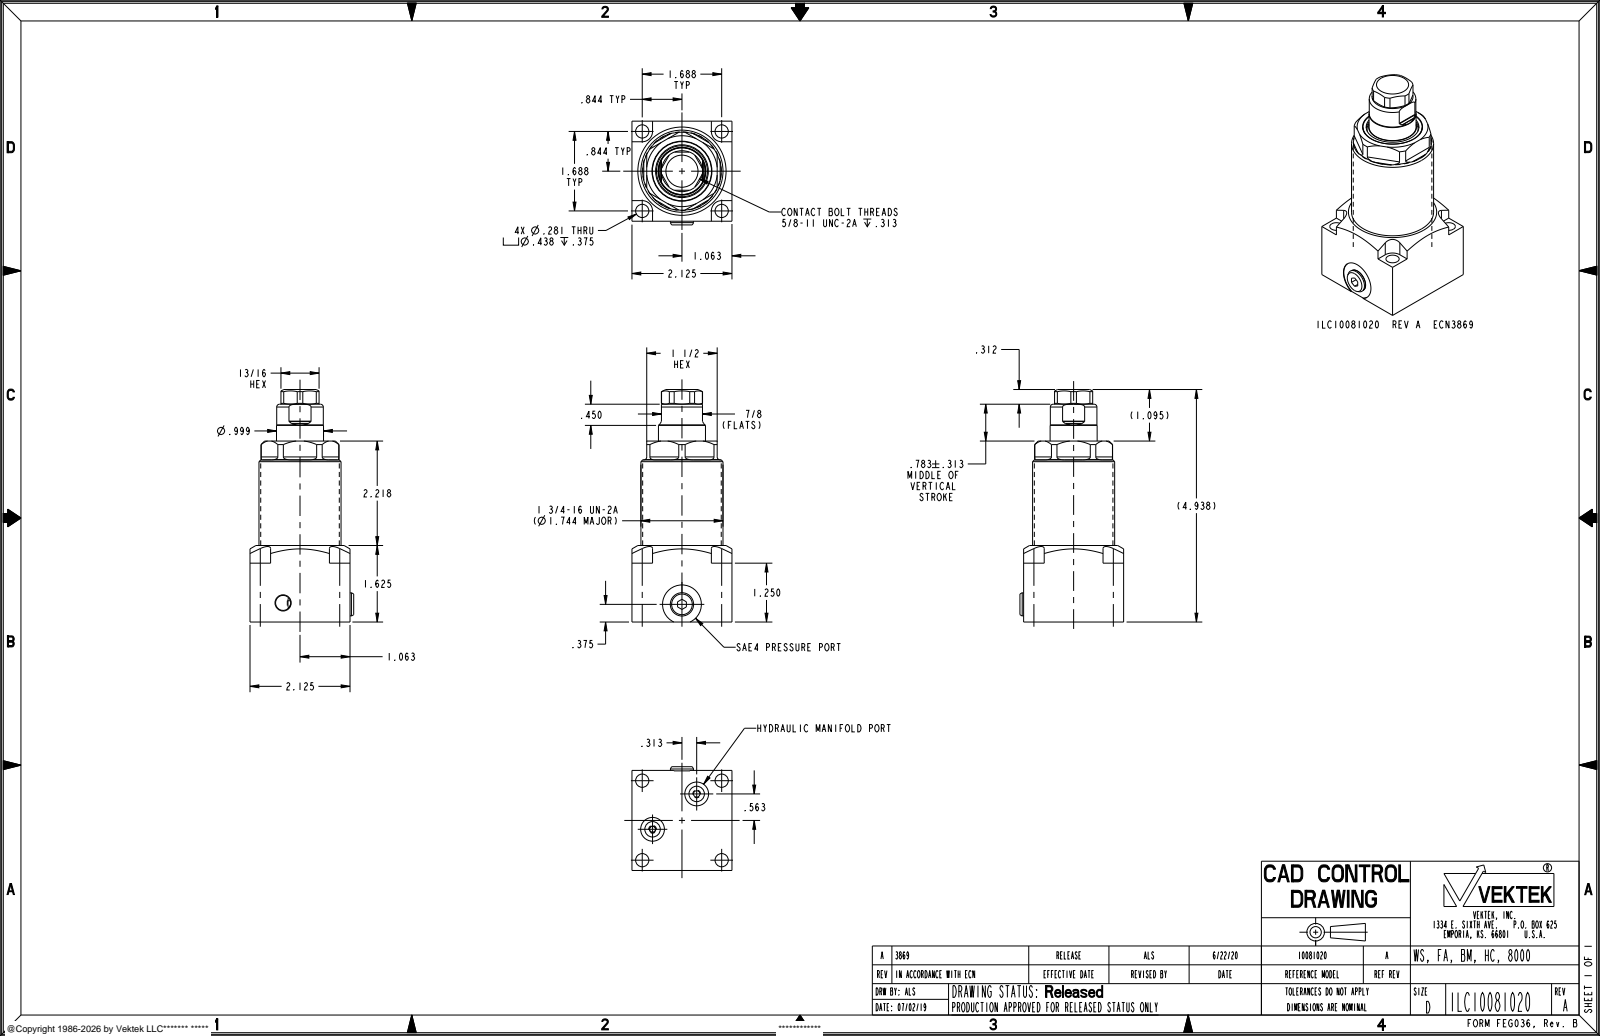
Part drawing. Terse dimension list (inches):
name: ILC10081020
written by: PRO/ENGINEER BY PARAMETRIC TECHNOLOGY CORPORATION, 2013320 (CONFIG_CONTROL_DESIGN)
unit: in
bodies: 1 solid, 193 faces (68 planar, 77 cylindrical, 48 other)
size: 4.938 × 2.204 × 2.125
volume: 12.4 in³; area: 60.04 in²
holes: 4× ⌀0.281, 2× ⌀0.136, 2× ⌀0.164, 2× ⌀0.328, 2× ⌀0.505, 1× ⌀0.125, 1× ⌀0.392, 1× ⌀0.825, 1× ⌀1.04, 1× ⌀1.12, 1× ⌀1.25
bosses: 1× ⌀1.744, 1× ⌀1.67, 1× ⌀1.256, 1× ⌀0.999, 1× ⌀0.99, 1× ⌀0.438, 1× ⌀0.437
rounds: 6× R0.063, 4× R0.02, 4× R0.219, 1× R0.437, 1× R0.828
face distances: 2.125, 1.497, 3.843, 1.25, 2.593, 0.437, 1.688, 0.314, 1.811, 1.625
hole spacings: 1.194, 1.688, 2.387, 0.601, 0.644, 0.653, 0.691, 1.055
